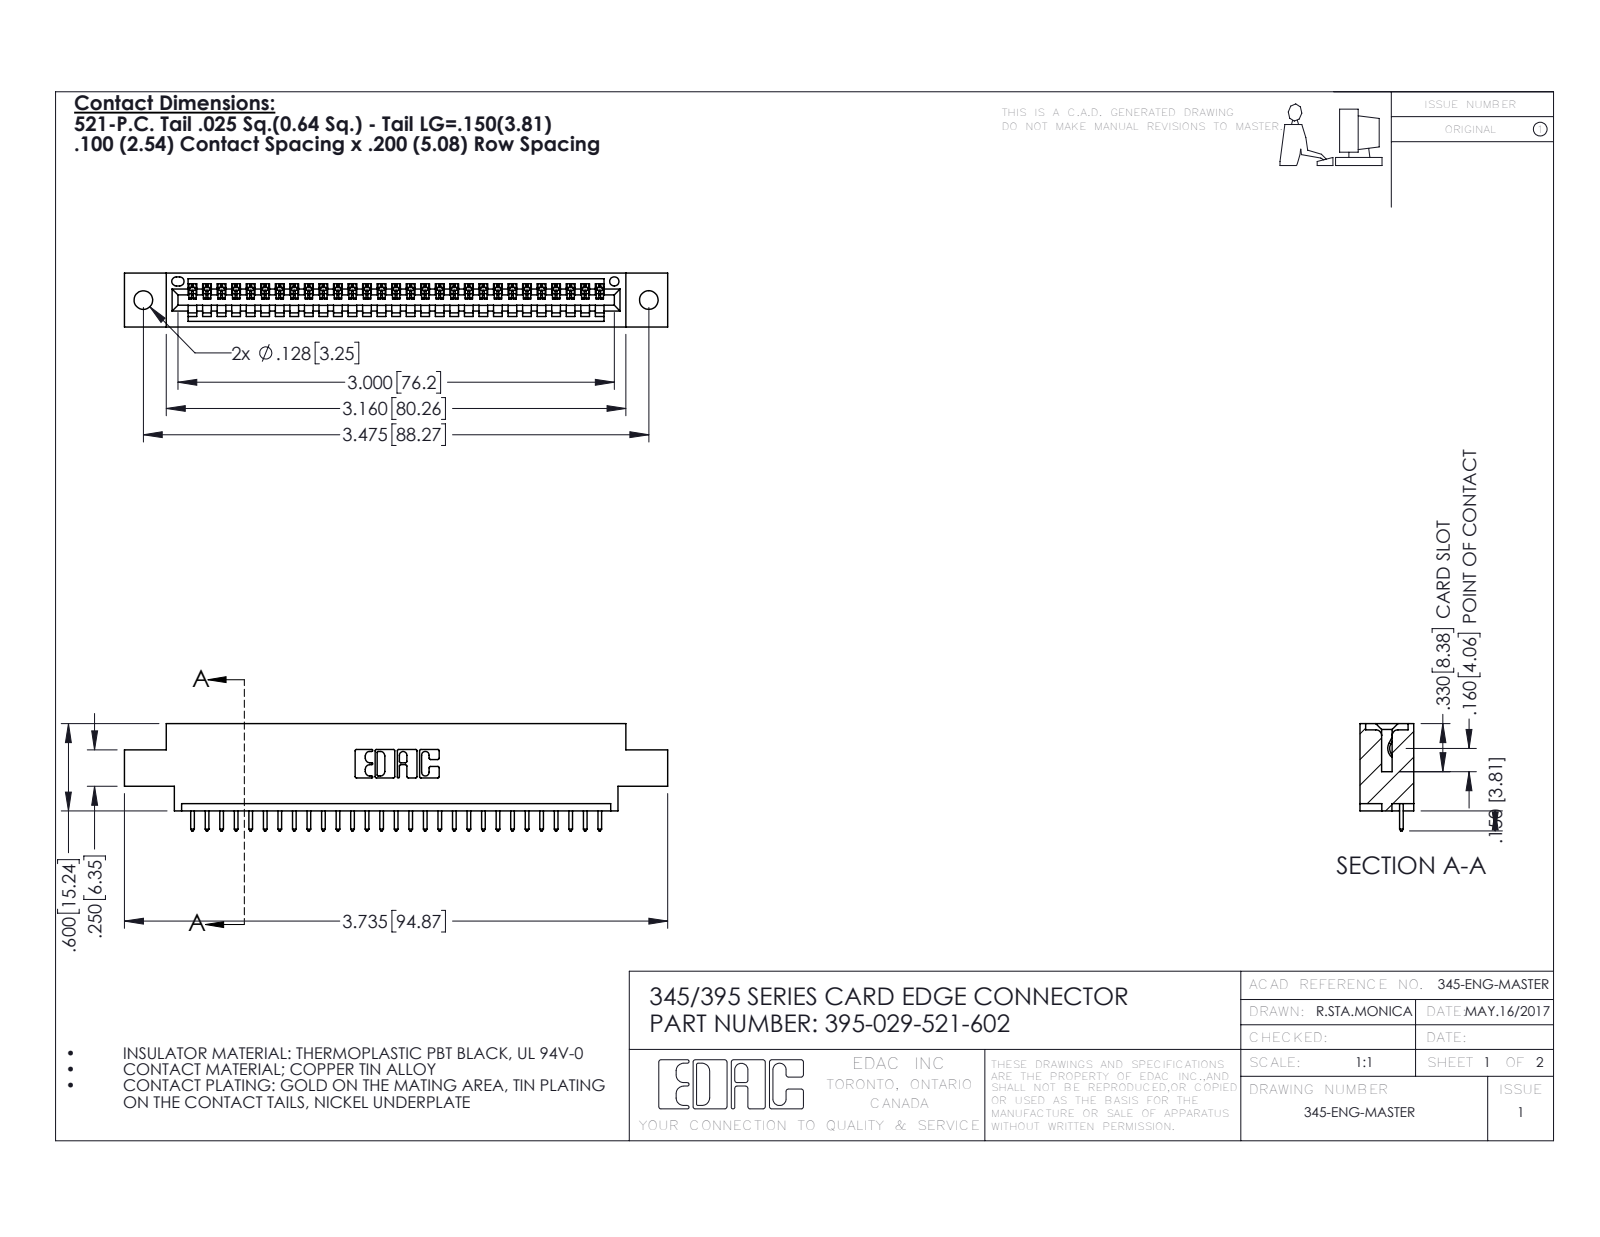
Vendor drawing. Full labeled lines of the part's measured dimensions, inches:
Part name (STEP PRODUCT): 345-292-001_345-293-121; 395-029-521-602; 345 Part_0.170 Offset - 0.128 Dia
STEP written by: SolidWorks 2016 (CONFIG_CONTROL_DESIGN)
Units: inches
Bodies: 30 solids, 1812 faces (1244 planar, 568 cylindrical, 0 other)
Overall size (bounding box): 3.735 × 0.737 × 0.37
Volume: 0.529 in³ · Surface area: 16.86 in²
Round holes (diameter × count): ⌀0.128 ×2, ⌀0.064 ×1
Partial cylindrical surfaces — rounded edges, fillets, slot ends (radius × count): R0.006 ×58, R0.01 ×58, R0.01 ×22, R0.007 ×6, R0.031 ×6, R0.026 ×3, R0.031 ×2, R0.04 ×2
Main face-to-face distances: 0.298, 0.072, 0.37, 0.2, 0.098, 0.272, 0.025, 0.225, 0.175, 0.149
Hole centre spacings: 0.27, 3.24, 3.475
